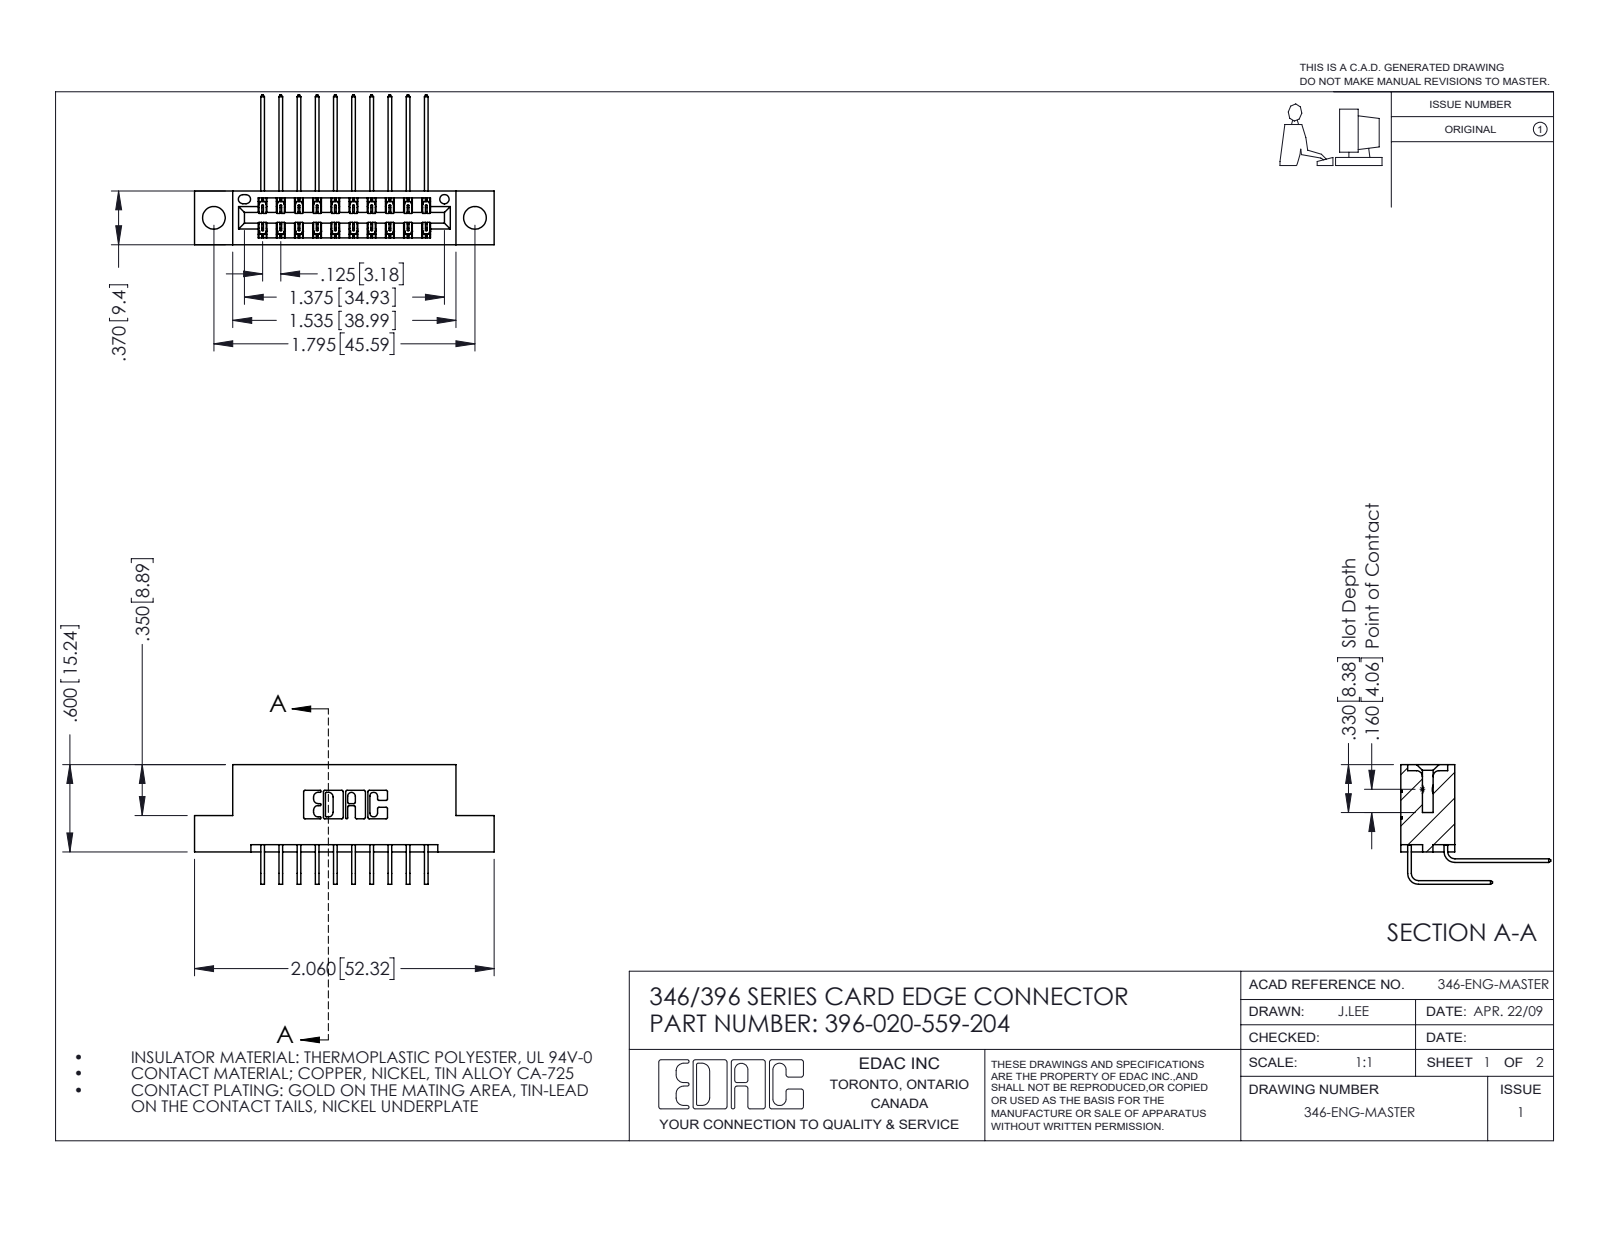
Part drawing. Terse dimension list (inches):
name: 396-020-559-204; 345-292-001_559 Tail - 2; 346 Part_Flush Mounting Lugs - 0.156 Dia-TH; 345-292-001_558 559 Tail - 1
written by: SolidWorks 2016 (CONFIG_CONTROL_DESIGN)
unit: in
bodies: 21 solids, 1202 faces (816 planar, 386 cylindrical, 0 other)
size: 2.06 × 1.03 × 0.823
volume: 0.298 in³; area: 10.19 in²
holes: 2× ⌀0.156, 1× ⌀0.064
rounds: 30× R0.006, 22× R0.01, 6× R0.007, 6× R0.031, 3× R0.026, 2× R0.014, 2× R0.022, 2× R0.024
face distances: 0.25, 0.048, 0.322, 0.37, 0.025, 0.072, 0.298, 0.275, 0.148, 0.222
hole spacings: 0.246, 1.59, 1.795
